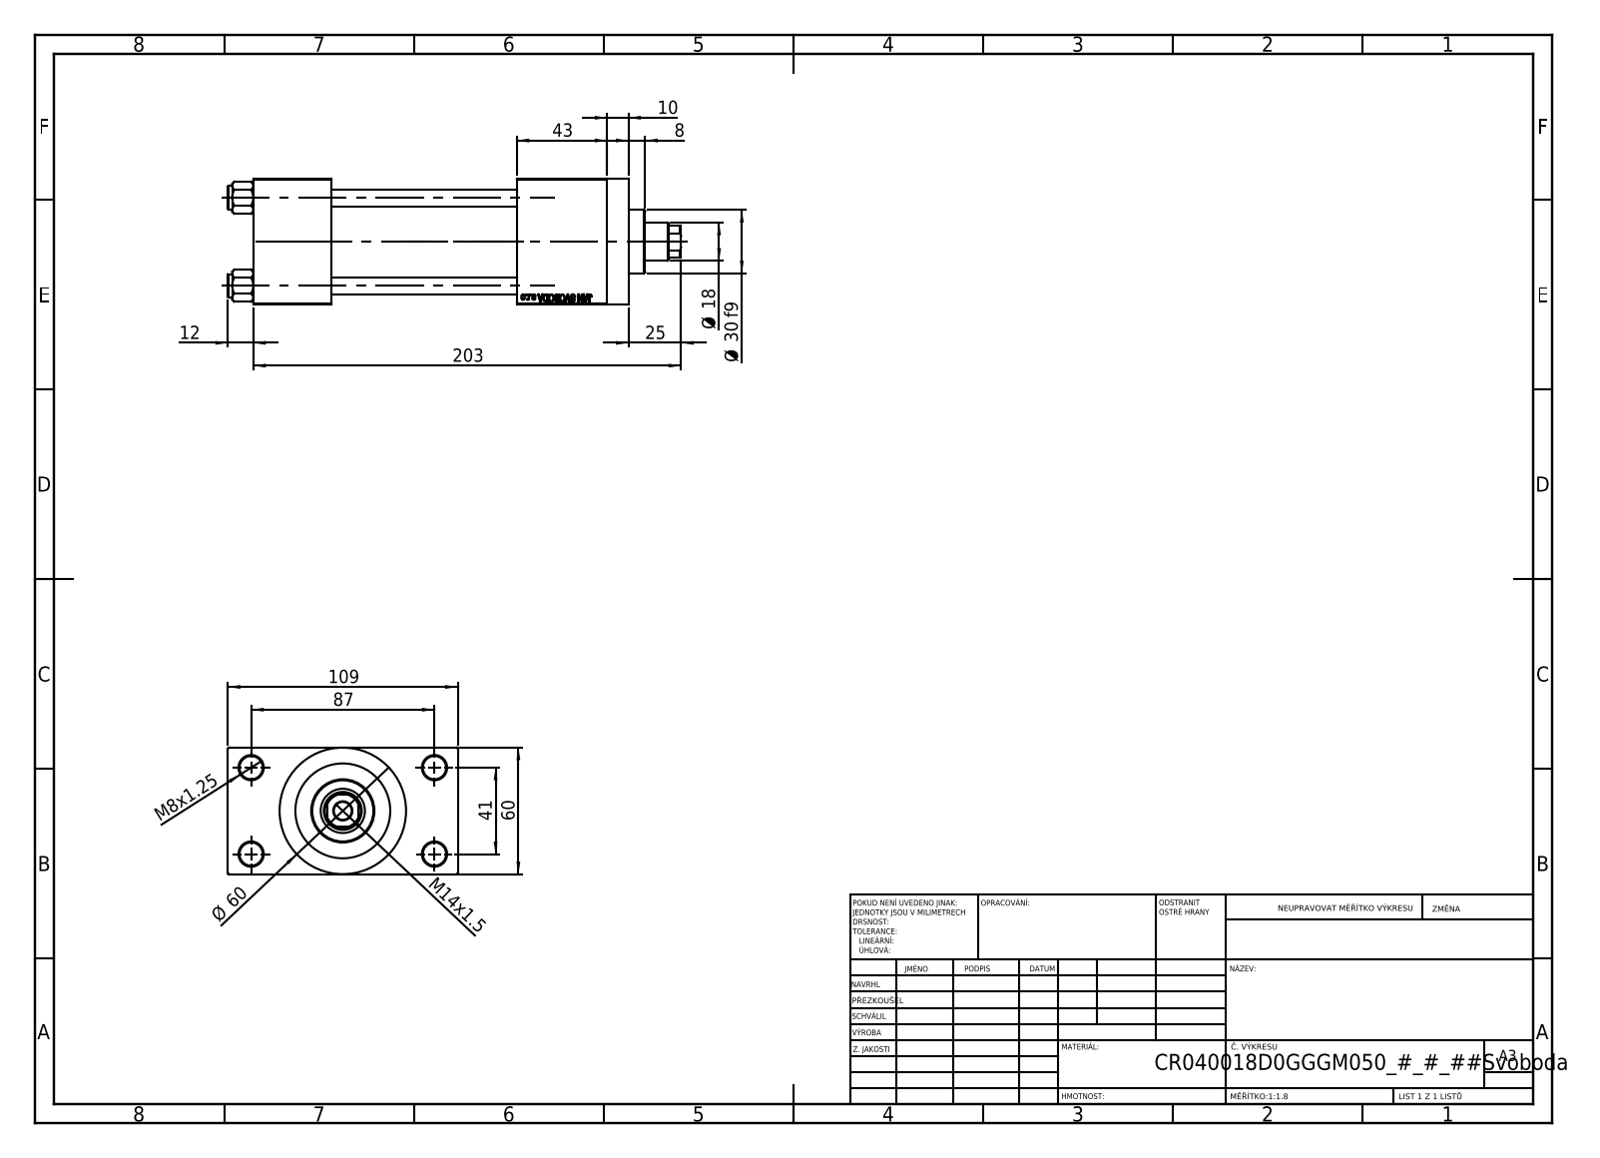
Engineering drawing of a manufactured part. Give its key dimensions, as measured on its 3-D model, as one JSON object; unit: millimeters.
{"part_name": "V215CR_VCP_D; NUT_M5_D; V215CR_D_TYCINKA; V215CR_D_Body (+1 more)", "step_written_by": "SolidWorks 2019 (CONFIG_CONTROL_DESIGN)", "units": "millimeters", "bodies": {"solids": 11, "faces": 1105, "planar": 498, "cylindrical": 89, "other": 518}, "overall_size": [215, 109, 60], "volume_mm3": 543590, "surface_area_mm2": 134085, "round_holes": [[8, 4], [11, 4], [7, 2], [16.66, 2], [24, 2], [8.5, 1], [18, 1], [21, 1], [31, 1], [40, 1], [45, 1]], "round_bosses_or_shafts": [[11, 4], [60, 1], [46, 1], [30, 1]], "partial_cylinders_radius": [[8.5, 1]], "face_to_face_distances": [60, 24.5, 84.5, 88, 37, 125, 168, 131, 43, 109], "hole_center_spacings": [22.65, 29.49, 41.7, 47.15, 48.09, 64.35, 76.49, 41]}
